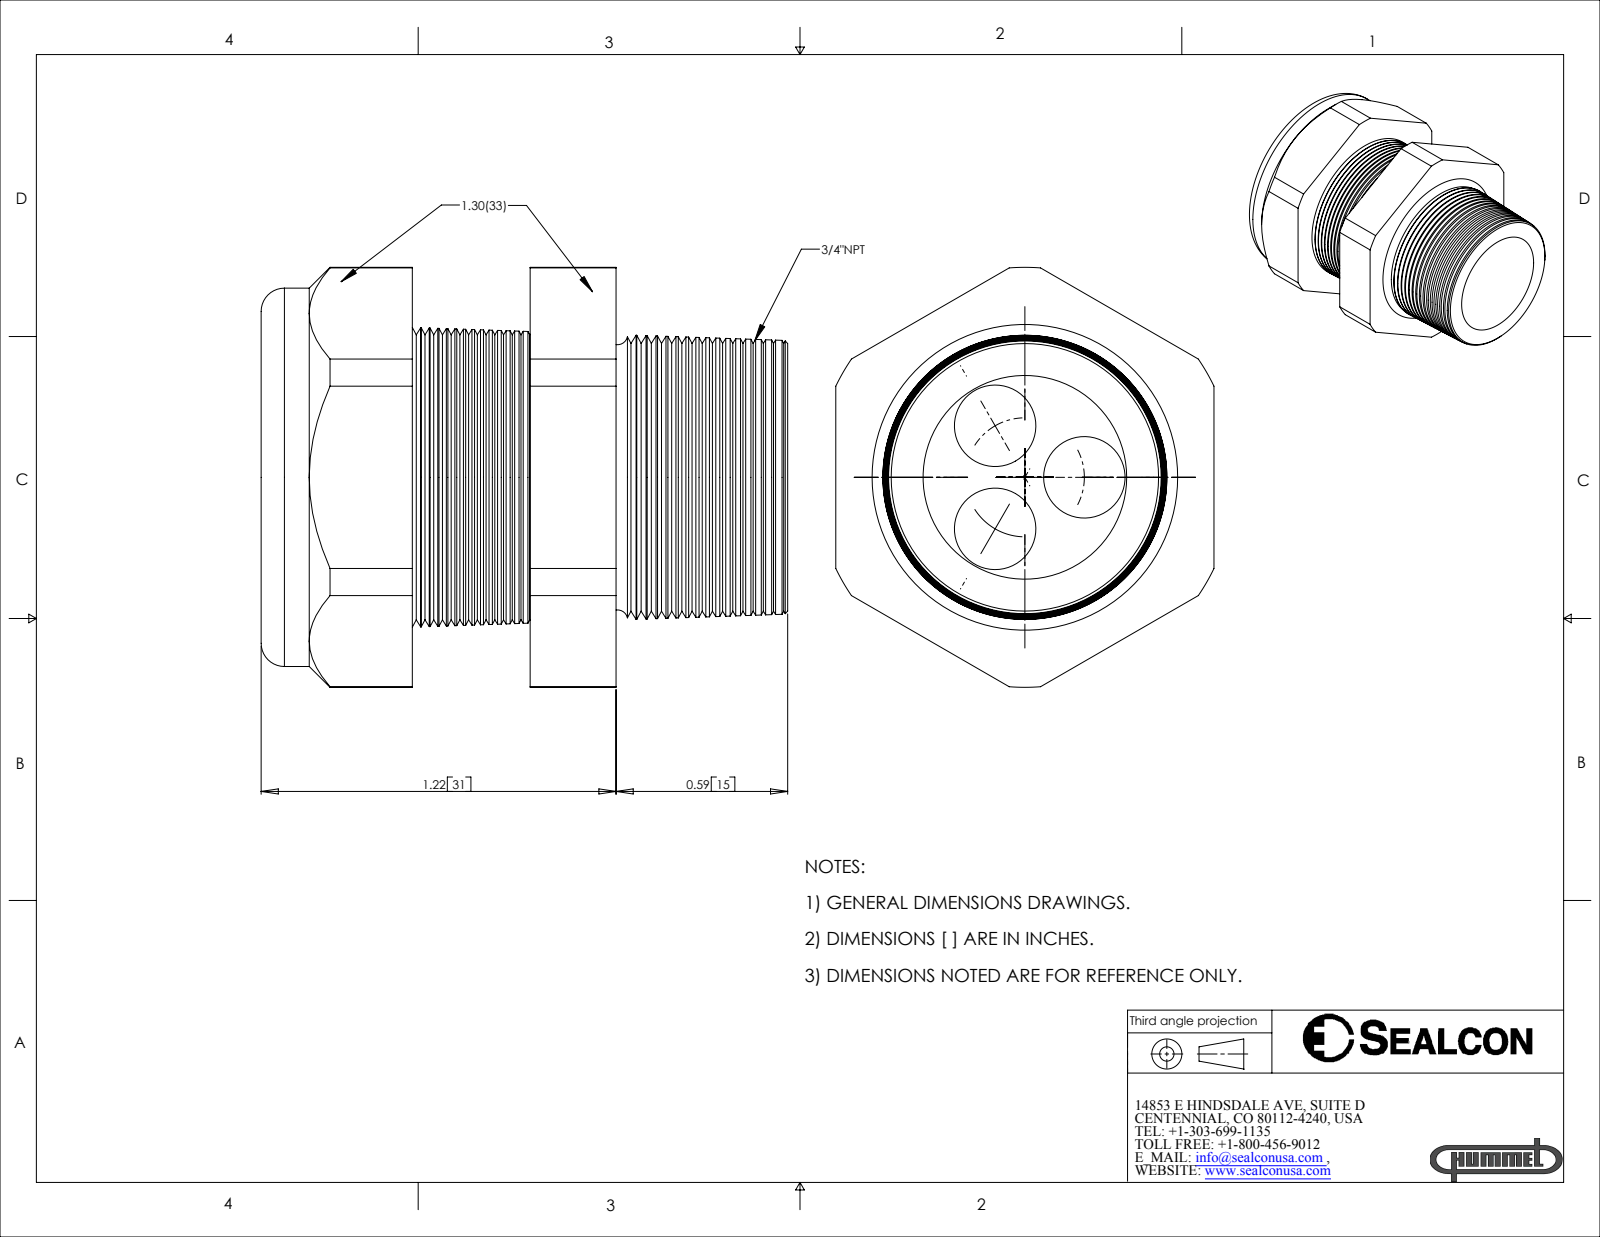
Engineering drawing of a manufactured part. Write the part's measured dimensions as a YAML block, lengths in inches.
part_name: "CD21N2-GY"
step_written_by: "SolidWorks 2007 (CONFIG_CONTROL_DESIGN)"
units: inches
bodies: {solids: 2, faces: 234, planar: 20, cylindrical: 26, other: 188}
overall_size: [1.77, 1.443, 1.3]
volume: 1.229
surface_area: 17.84
round_holes:
  - {diameter: 0.28, count: 3}
  - {diameter: 0.69, count: 1}
  - {diameter: 0.71, count: 1}
round_bosses_or_shafts:
  - {diameter: 1.3, count: 1}
partial_cylinders:
  - {radius: 0.721, count: 1}
face_to_face_distances: [1.3, 0.925, 0.52, 0.405, 1.22, 0.7, 0.295, 1.77, 1.25, 0.845]
hole_center_spacings: [0.354, 0.205, 0.204]
